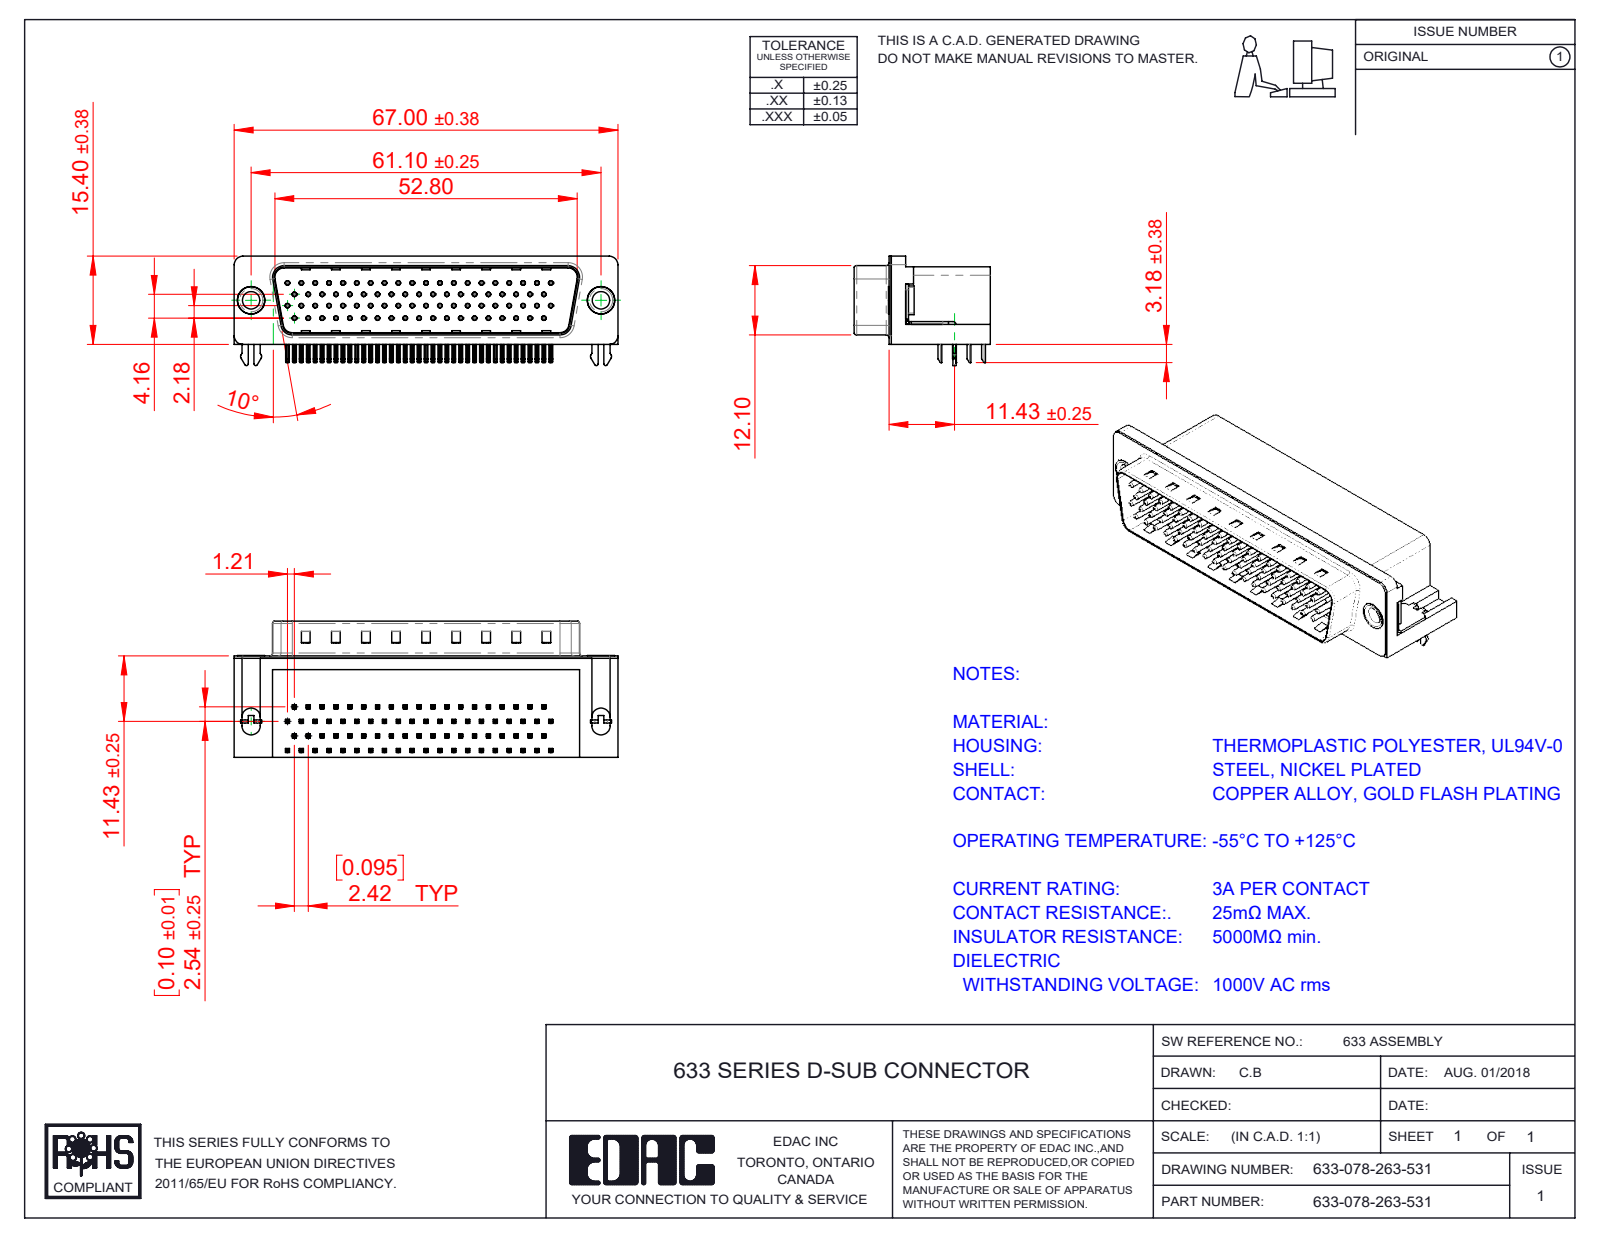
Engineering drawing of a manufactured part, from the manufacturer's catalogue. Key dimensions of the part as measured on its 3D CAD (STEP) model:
Part name (STEP PRODUCT): 633 Housing_78 Contact; 633 Thru Hole Rivet; 633 2 Prong Board Lock_78 Contact; 633 Shell_78 Contact (+5 more)
STEP written by: SolidWorks 2016 (CONFIG_CONTROL_DESIGN)
Units: millimetres
Bodies: 84 solids, 6276 faces (4013 planar, 1768 cylindrical, 495 other)
Overall size (bounding box): 67 × 23.8 × 19.1
Volume: 14 601 mm³ · Surface area: 16 339 mm²
Round holes (diameter × count): ⌀0.35 ×78, ⌀0.8 ×78, ⌀3.05 ×2, ⌀4 ×2, ⌀4.8 ×2, ⌀5 ×2
Round bosses / shafts (diameter × count): ⌀0.75 ×78, ⌀4.9 ×2, ⌀4.75 ×2, ⌀3.85 ×2
Partial cylindrical surfaces — rounded edges, fillets, slot ends (radius × count): R0.25 ×320, R0.12 ×156, R1 ×16, R0.5 ×14, R1.6 ×8, R1.5 ×6, R0.32 ×4, R0.45 ×4
Main face-to-face distances: 0.4, 13.2, 17.3, 11.7, 13.35, 2.05, 13.75, 1.65, 1.85, 11.9
Hole centre spacings: 2.42, 4.84, 7.26, 9.68, 6.26, 7.13, 12.1, 8.62
